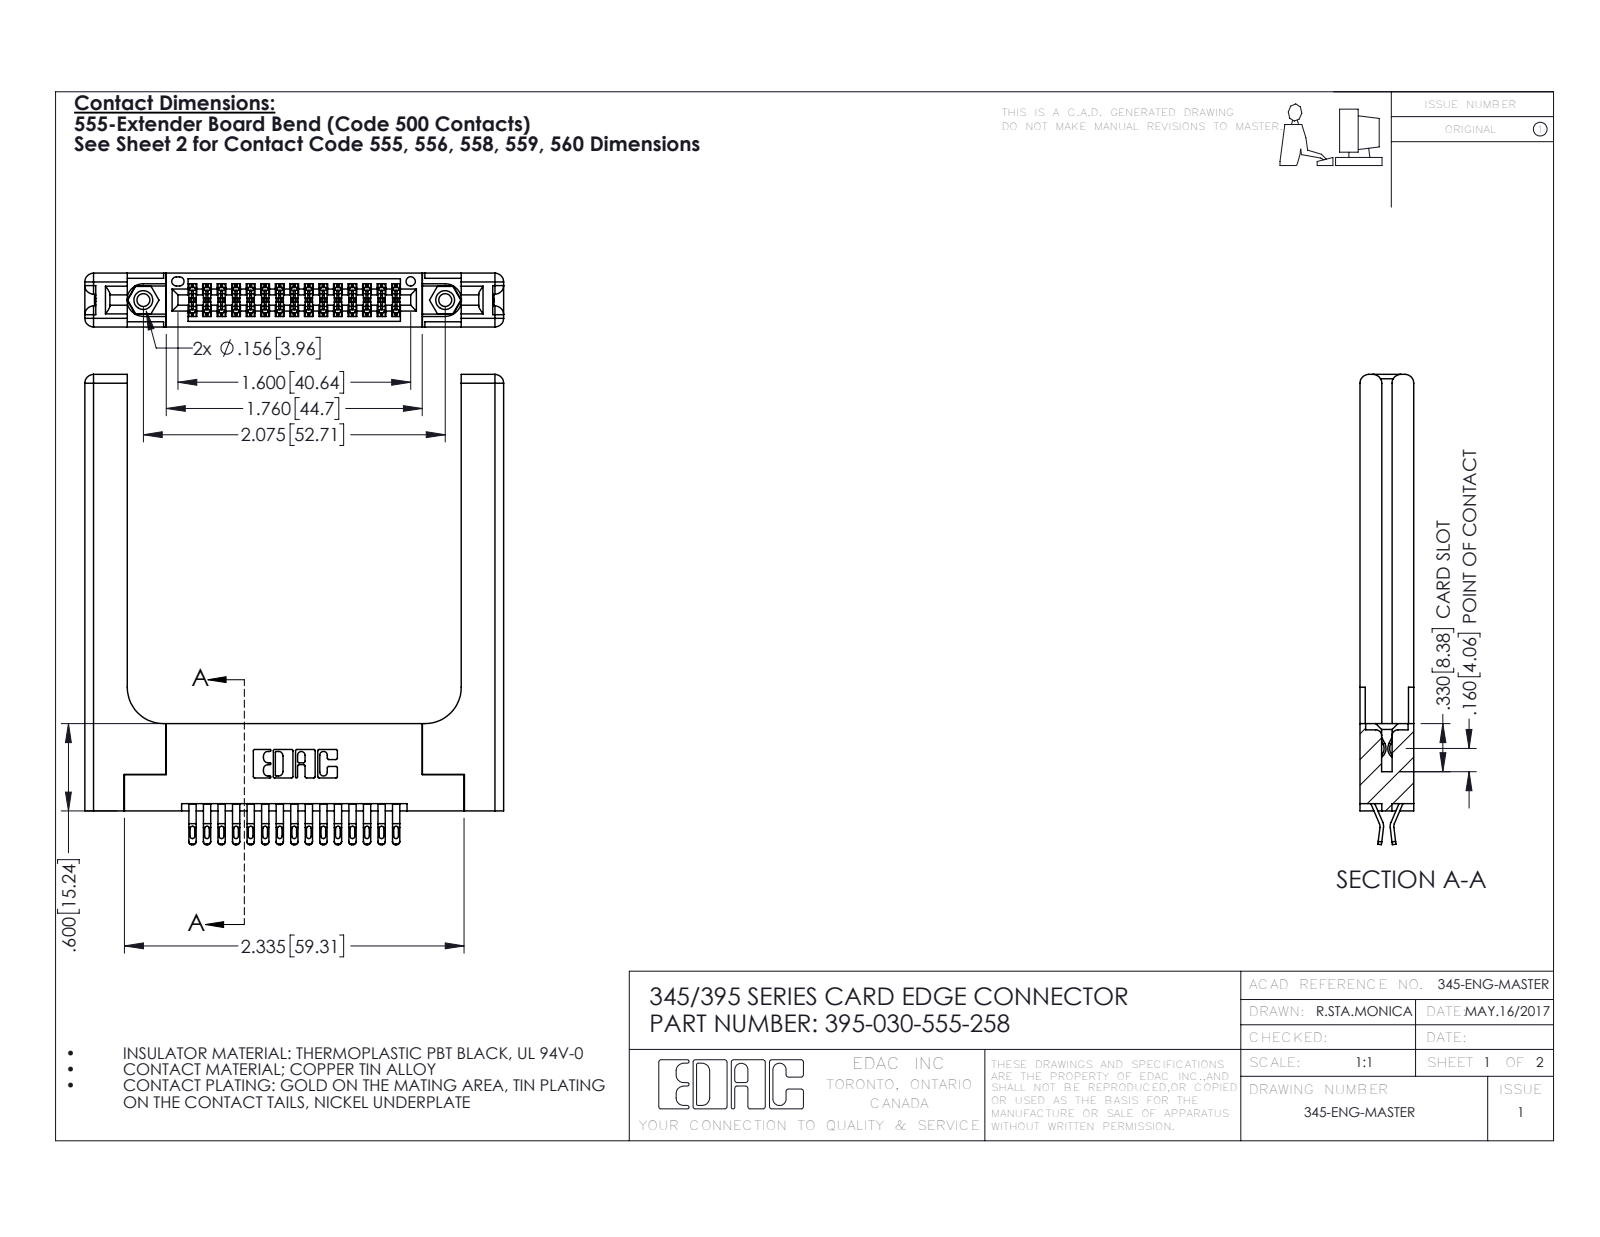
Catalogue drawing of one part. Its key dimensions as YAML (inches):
part_name: "345-220-058_345-220-058; 345-250-001_345-250-001-102; 395-030-555-258; 345-292-001_555 Tail (+1 more)"
step_written_by: "SolidWorks 2016 (CONFIG_CONTROL_DESIGN)"
units: inches
bodies: {solids: 35, faces: 2062, planar: 1158, cylindrical: 844, other: 60}
overall_size: [3.232, 2.879, 0.37]
volume: 0.941
surface_area: 23.4
round_holes:
  - {diameter: 0.089, count: 2}
  - {diameter: 0.125, count: 2}
  - {diameter: 0.156, count: 2}
  - {diameter: 0.064, count: 1}
round_bosses_or_shafts:
  - {diameter: 0.155, count: 2}
partial_cylinders:
  - {radius: 0.016, count: 75}
  - {radius: 0.02, count: 60}
  - {radius: 0.006, count: 45}
  - {radius: 0.01, count: 22}
  - {radius: 0.06, count: 16}
  - {radius: 0.007, count: 6}
  - {radius: 0.031, count: 6}
  - {radius: 0.026, count: 3}
face_to_face_distances: [0.37, 0.072, 0.298, 0.077, 0.148, 0.15, 0.22, 0.2, 0.025, 0.225]
hole_center_spacings: [0.27, 1.842, 2.075]
